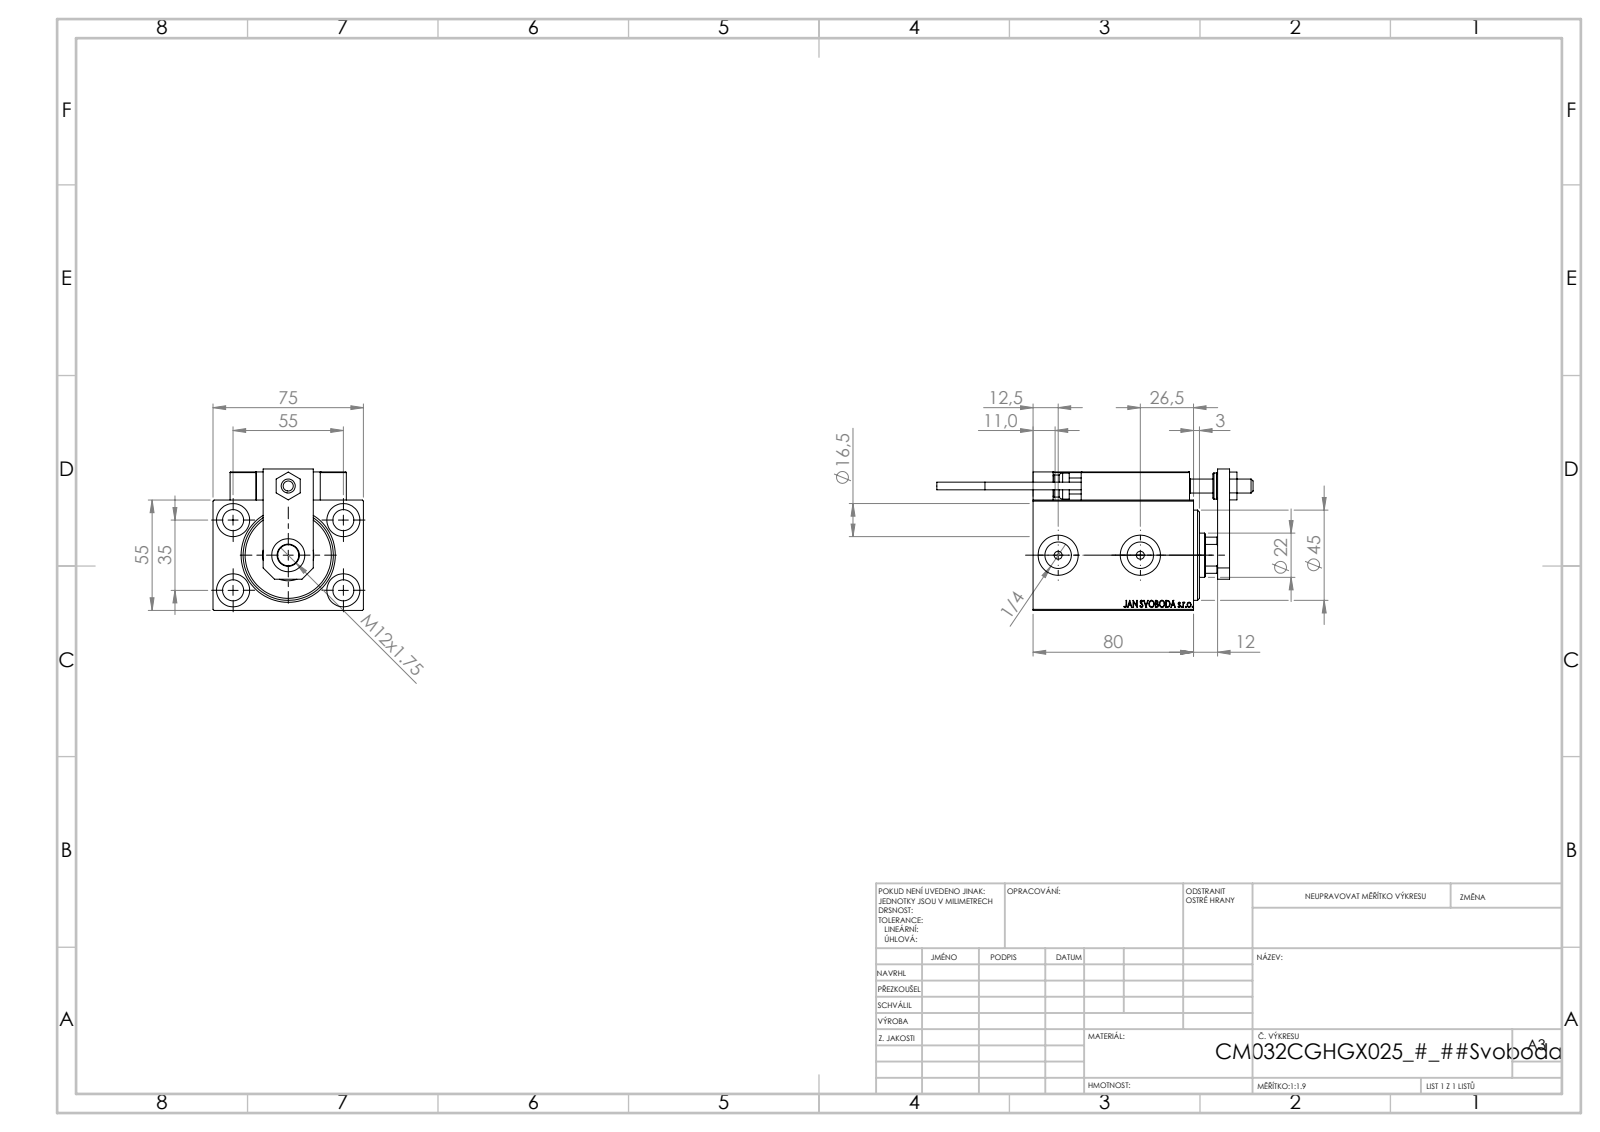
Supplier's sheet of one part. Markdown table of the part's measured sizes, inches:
| quantity | value |
| --- | --- |
| part name | SWITCH_X_FRONT_BACK; NUT_D12; MAGNET; Block (+8 more) |
| STEP written by | SolidWorks 2019 (CONFIG_CONTROL_DESIGN) |
| units | inches |
| bodies | 23 solids, 1282 faces (560 planar, 188 cylindrical, 534 other) |
| overall size | 6.209 × 2.953 × 2.776 |
| volume | 20.15 in³ |
| surface area | 135.5 in² |
| round holes (diameter × count) | 0.157 × 6, 0.315 × 5, 0.413 × 5, 0.65 × 5, 0.126 × 4, 0.197 × 2, 0.518 × 2, 0.787 × 2, 0.276 × 1, 0.866 × 1, 1.004 × 1, 1.26 × 1 |
| round bosses / shafts (diameter × count) | 0.197 × 2, 0.15 × 2, 0.512 × 1, 0.433 × 1 |
| partial cylindrical surfaces (radius × count) | 0.012 × 30, 0.118 × 2, 0.413 × 1 |
| main face-to-face distances | 2.165, 2.953, 0.551, 0.394, 2.717, 0.472, 0.984, 2.283, 0.276, 0.591 |
| hole center spacings | 1.283, 0.448, 0.787, 1.165, 1.169, 1.262, 1.273, 1.378 |
